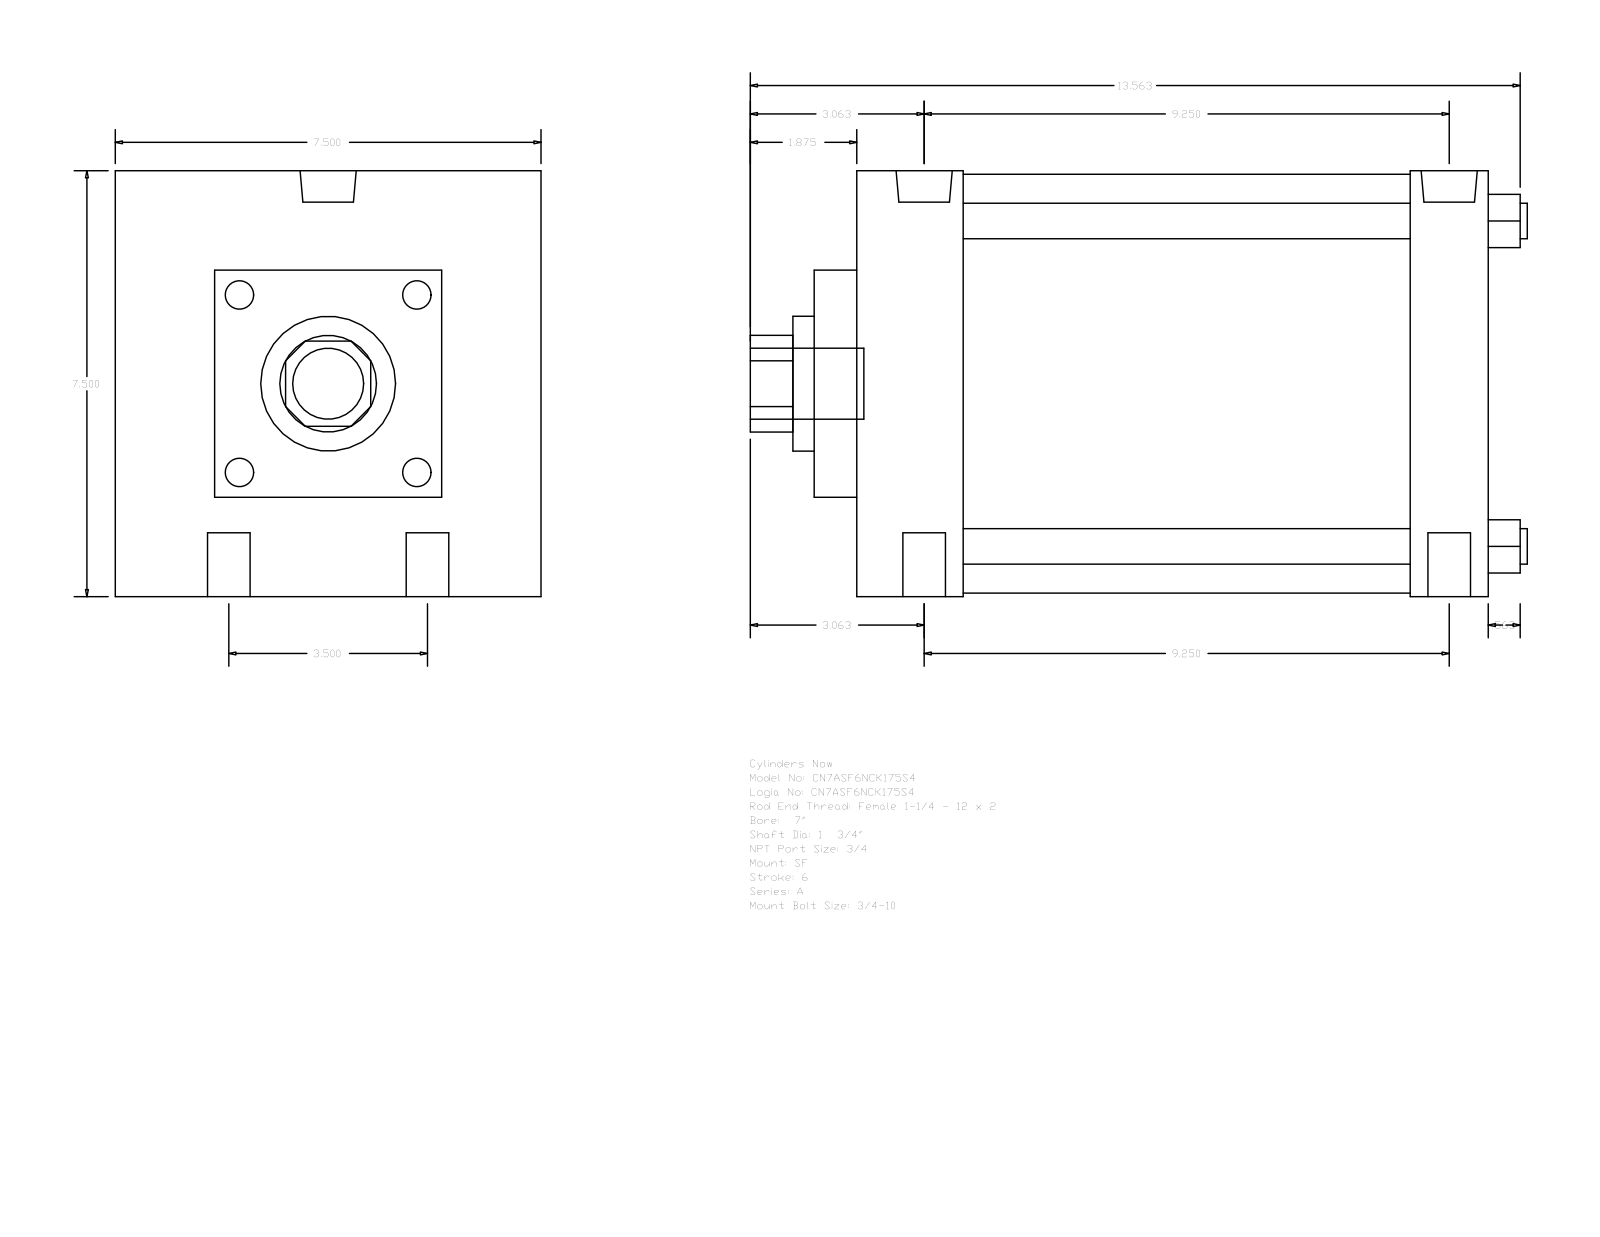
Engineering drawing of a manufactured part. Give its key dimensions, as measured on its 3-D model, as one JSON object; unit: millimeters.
{"part_name": "A_SF__0700_1.75", "step_written_by": "GSSL Pune (CONFIG_CONTROL_DESIGN)", "units": "millimeters", "bodies": {"solids": 0, "faces": 93, "planar": 67, "cylindrical": 26, "other": 0}, "overall_size": [347.66, 190.5, 190.5], "round_holes": [[19.05, 4], [15.08, 2], [25.12, 2], [44.45, 1], [60.33, 1]], "round_bosses_or_shafts": [[15.88, 4], [187.32, 1], [31.75, 1]], "partial_cylinders_radius": [[21.63, 1]], "face_to_face_distances": [190.5, 282.58, 44.45, 19.05, 47.63, 247.65, 200.02, 234.95, 34.93, 146.05], "hole_center_spacings": [44.45, 239.12, 234.95, 88.9, 251.21, 223.83]}
